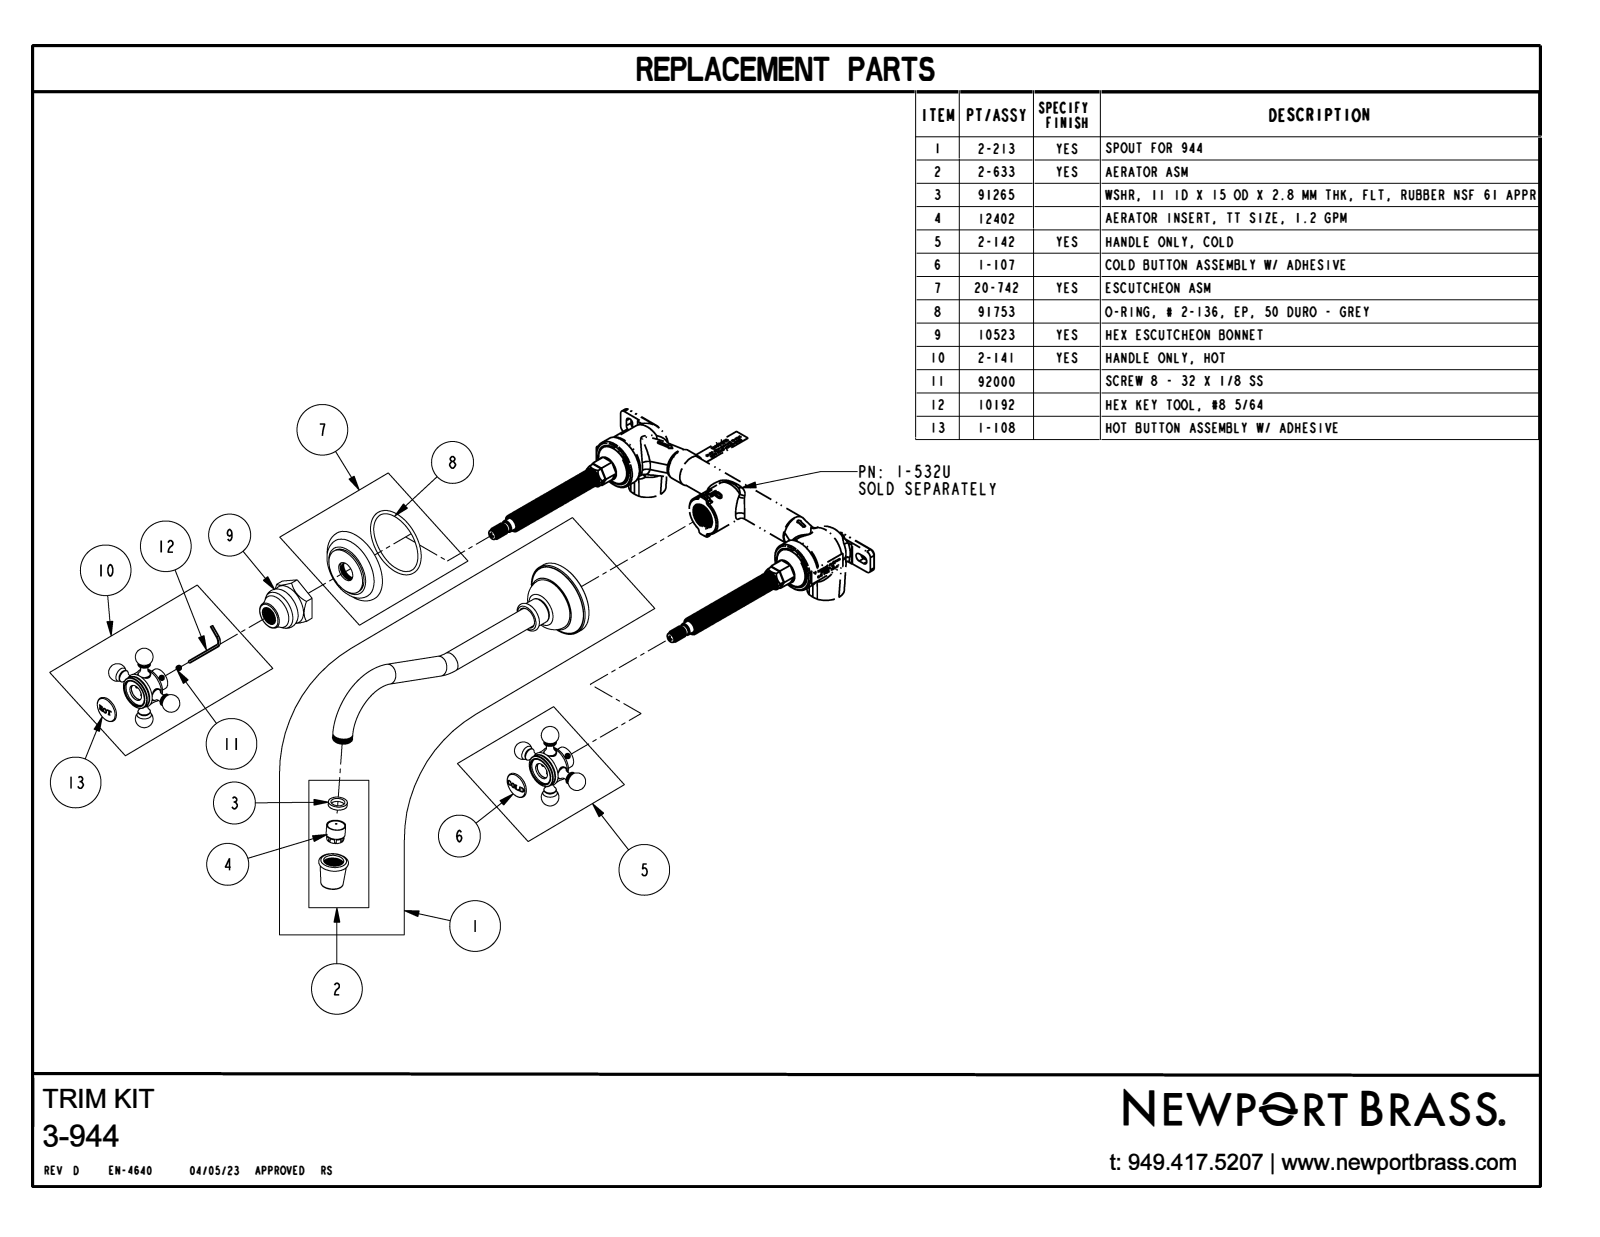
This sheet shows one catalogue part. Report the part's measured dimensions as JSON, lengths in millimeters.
{"part_name": "3-944_S", "step_written_by": "CREO PARAMETRIC BY PTC INC, 2018400 (AUTOMOTIVE_DESIGN)", "units": "millimeters", "bodies": {"solids": 3, "faces": 435, "planar": 125, "cylindrical": 94, "other": 216}, "overall_size": [274, 258.9, 74], "volume_mm3": 235600, "surface_area_mm2": 53720, "round_holes": [[10.4, 4]], "round_bosses_or_shafts": [[10, 4], [37.6, 2], [26.8, 2], [17.4, 2], [15.9, 2], [59.9, 1], [44.8, 1], [20.7, 1]], "partial_cylinders_radius": [[0.2, 7], [0.6, 7], [0.8, 5], [1.2, 3], [0.5, 2], [0.9, 2], [1, 2], [1.4, 1]], "face_to_face_distances": [33.4, 9.5, 24.4, 14.9, 33.4, 11.1, 1.6, 13.3, 13.2, 3.7], "hole_center_spacings": [200]}
